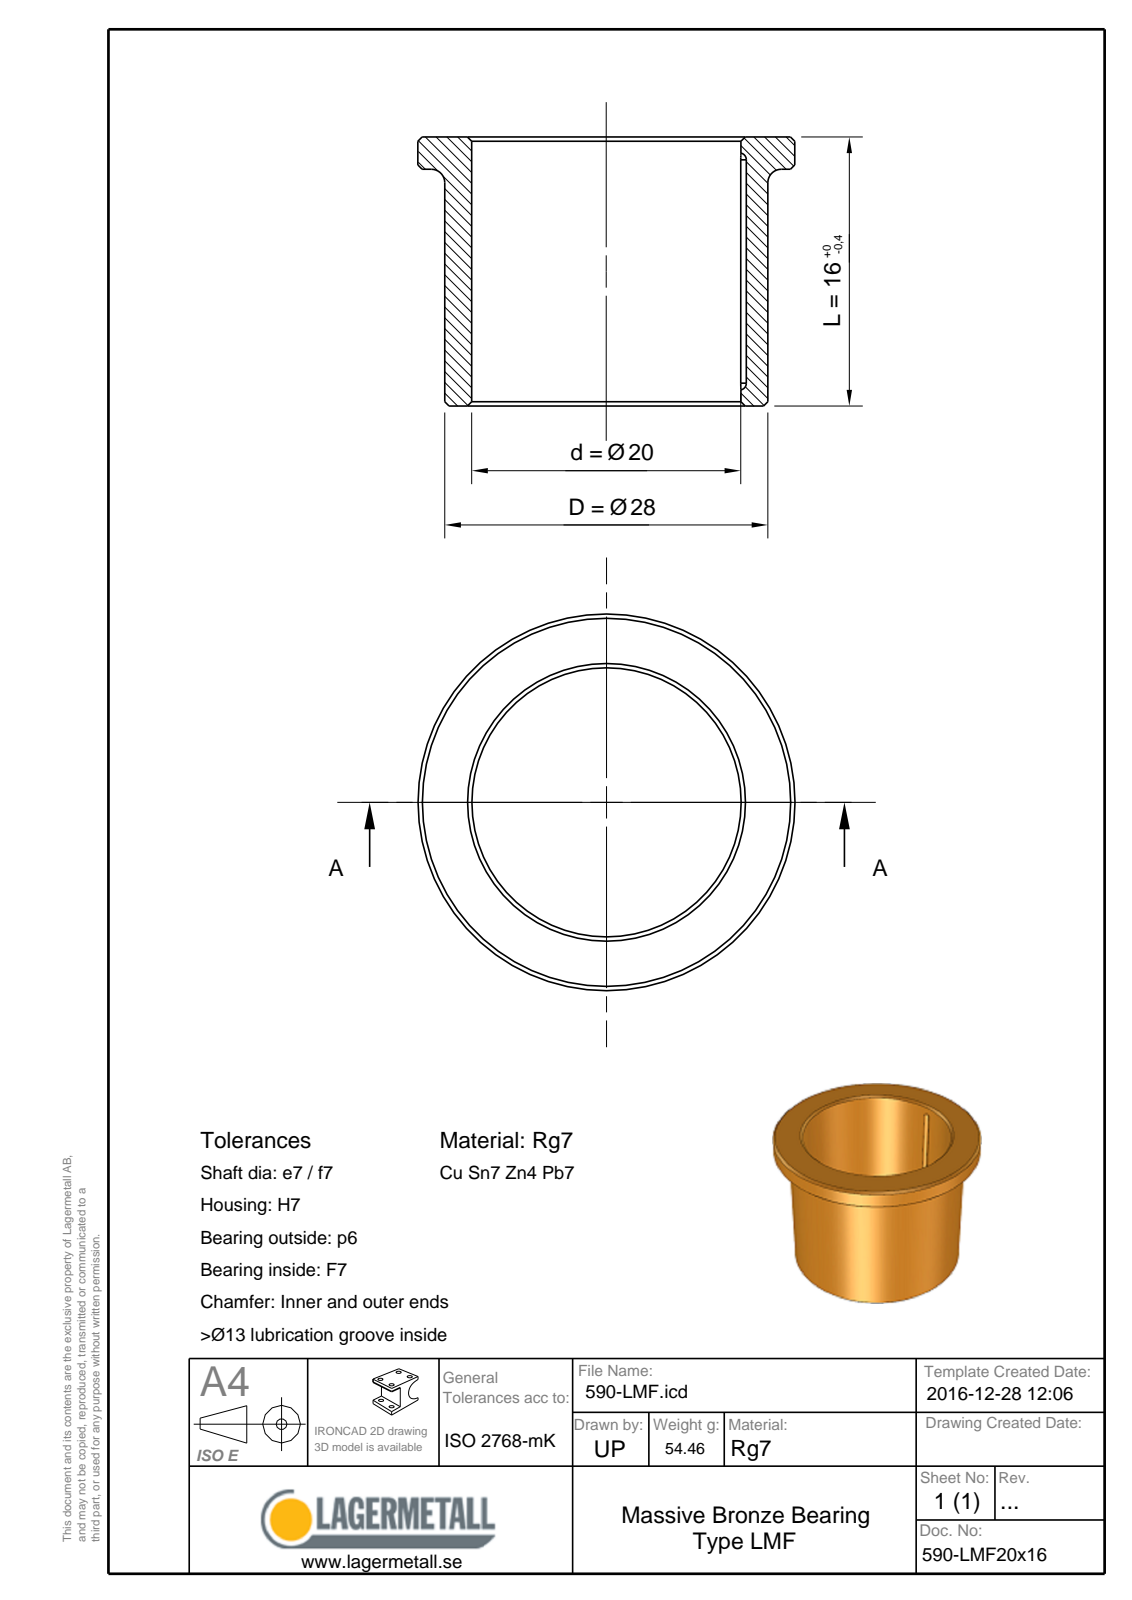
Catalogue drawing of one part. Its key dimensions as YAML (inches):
part_name: "590-LMF20x16"
step_written_by: "Spatial InterOp 3D (CONFIG_CONTROL_DESIGN)"
units: inches
bodies: {solids: 1, faces: 19, planar: 5, cylindrical: 6, other: 8}
overall_size: [1.378, 1.378, 0.63]
volume: 0.378
surface_area: 5.625
round_holes:
  - {diameter: 0.787, count: 1}
round_bosses_or_shafts:
  - {diameter: 1.378, count: 1}
  - {diameter: 1.102, count: 1}
partial_cylinders:
  - {radius: 0.03, count: 3}
face_to_face_distances: [0.63, 0.472, 0.157, 0.059]
